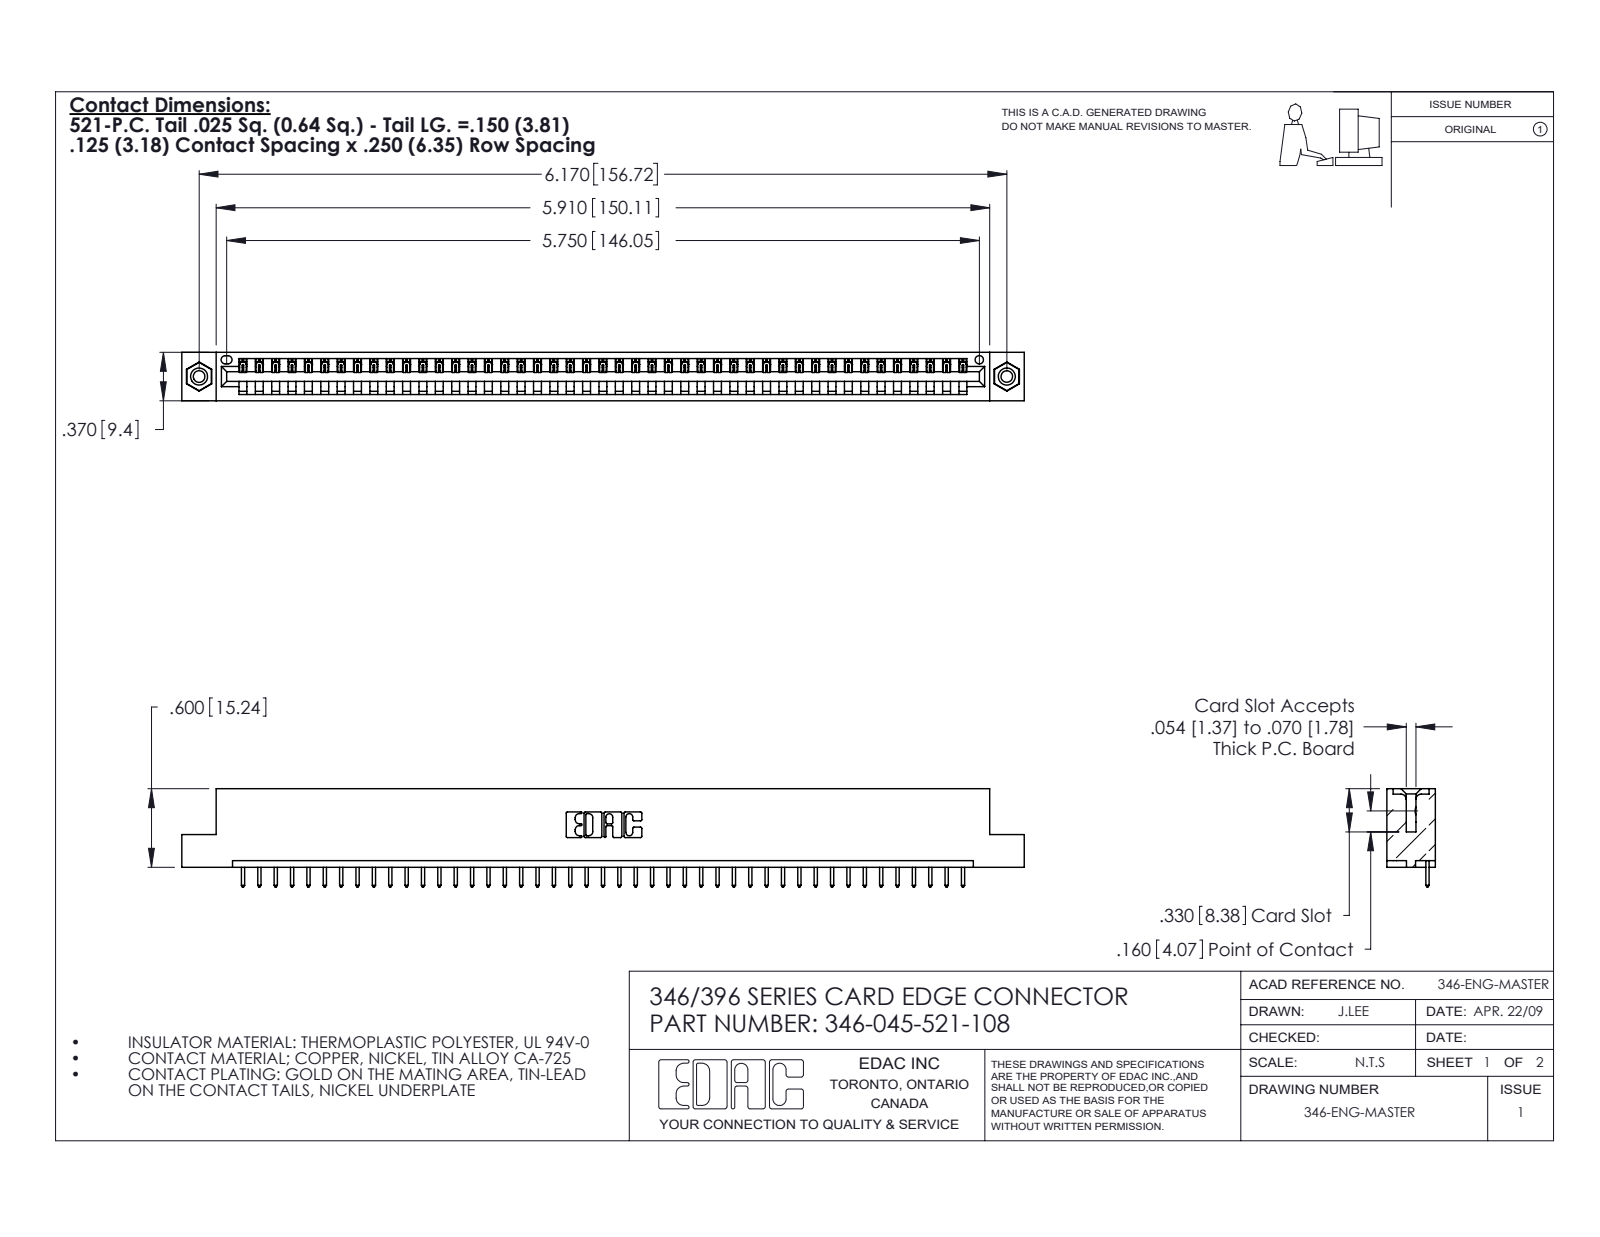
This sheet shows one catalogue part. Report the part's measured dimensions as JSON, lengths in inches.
{"part_name": "345-250-001_345-250-003-102; 345-292-001_345-293-121; 346 Part_Flush Mounting Lugs - 0.156 Dia-TI; 346-045-521-108", "step_written_by": "SolidWorks 2020 (CONFIG_CONTROL_DESIGN)", "units": "inches", "bodies": {"solids": 48, "faces": 2792, "planar": 1908, "cylindrical": 868, "other": 16}, "overall_size": [6.435, 0.75, 0.37], "volume_in3": 0.948, "surface_area_in2": 29.38, "round_holes": [[0.089, 2], [0.125, 2], [0.156, 2], [0.064, 1]], "round_bosses_or_shafts": [[0.155, 2]], "partial_cylinders_radius": [[0.006, 90], [0.01, 90], [0.01, 22], [0.007, 6], [0.031, 6], [0.026, 3], [0.031, 2], [0.04, 2]], "face_to_face_distances": [0.048, 0.322, 0.37, 0.25, 0.072, 0.298, 0.025, 0.148, 0.222, 0.1], "hole_center_spacings": [0.246, 5.961, 6.17]}
